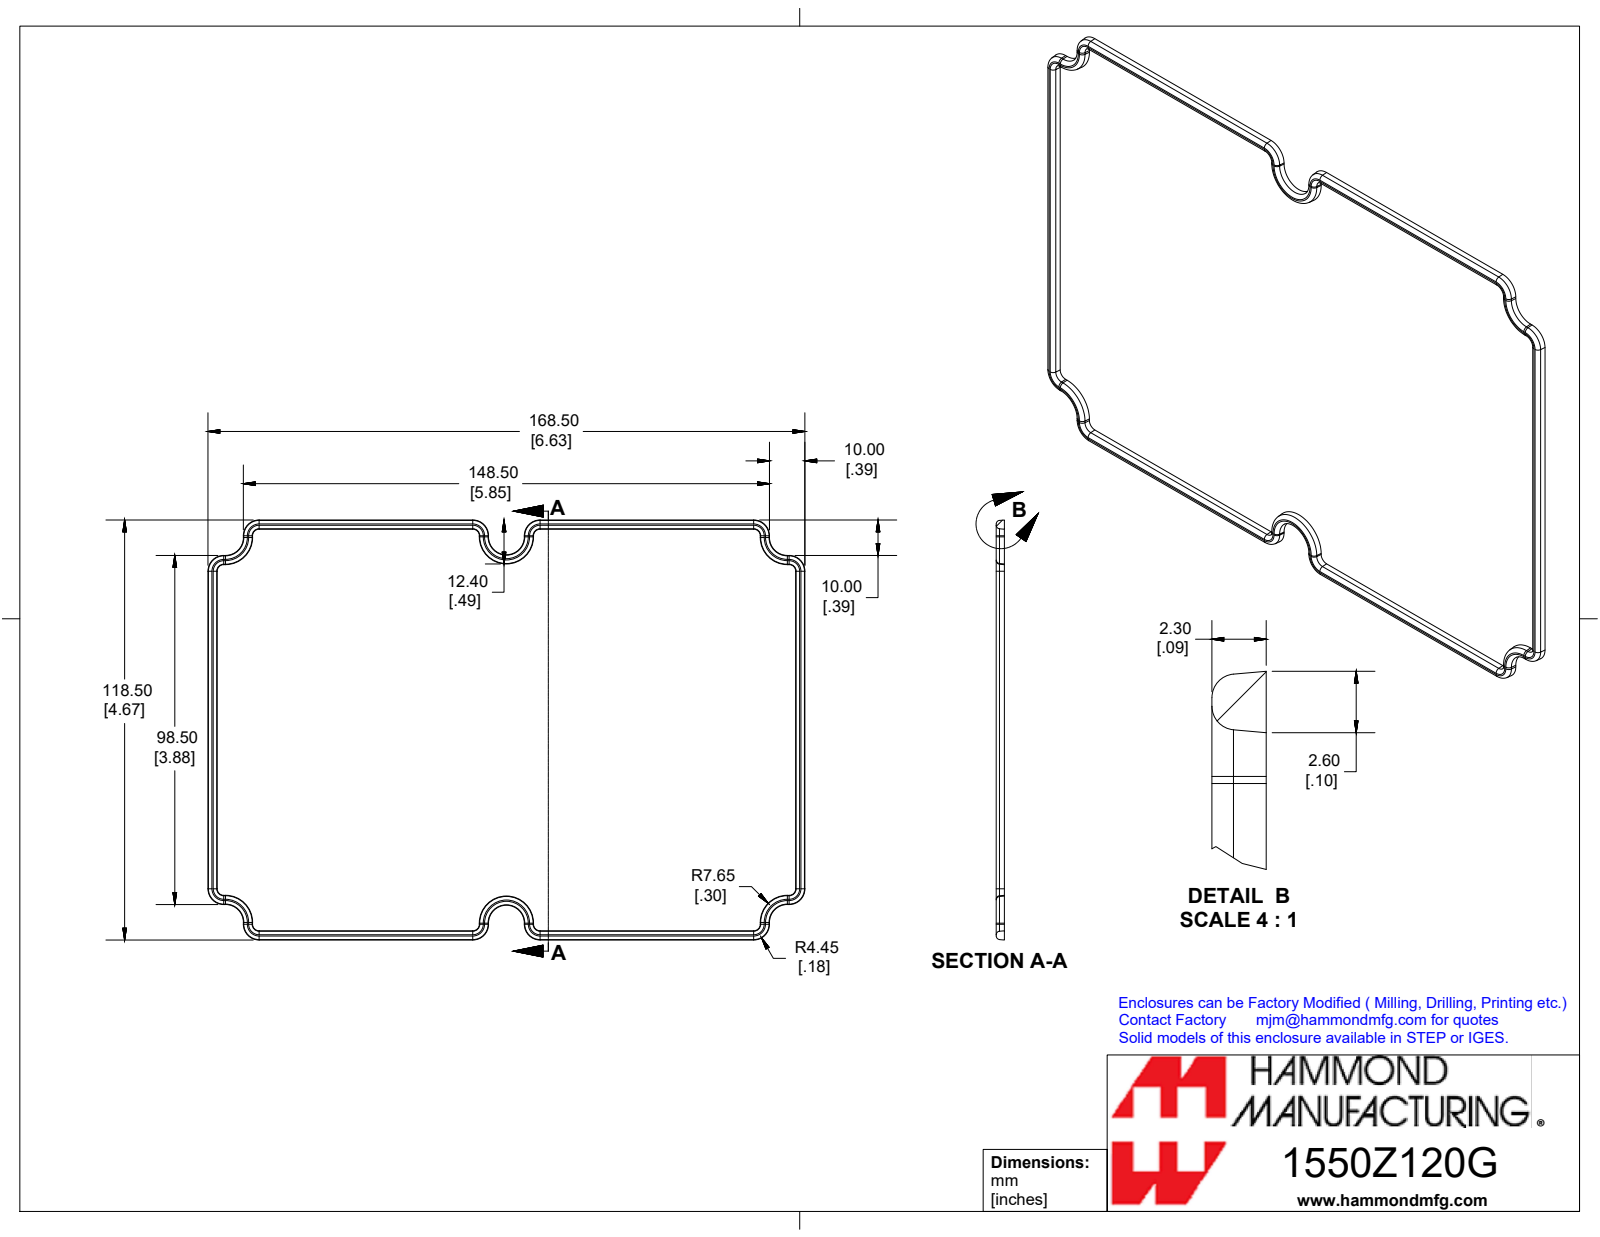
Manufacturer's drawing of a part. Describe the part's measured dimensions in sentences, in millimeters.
The part is named "1550Z120GASKET". Its 3-D file was written by "SolidWorks 2019 (CONFIG_CONTROL_DESIGN)". It is 1 solid with 203 faces: 53 planar, 36 cylindrical and 114 other. Overall it measures 168.5 by 118.5 by 2.4 millimeters. Its volume is 2 920 cubic millimeters and its surface area 4 925 square millimeters. Partial cylindrical surfaces (rounded edges, fillets, slot ends): 20 of radius 1. The main face-to-face distances are 115.4, 165.2, 2.3, 10, 155.3, 105.5, 2.4, 76.3, 66.3, 89.
